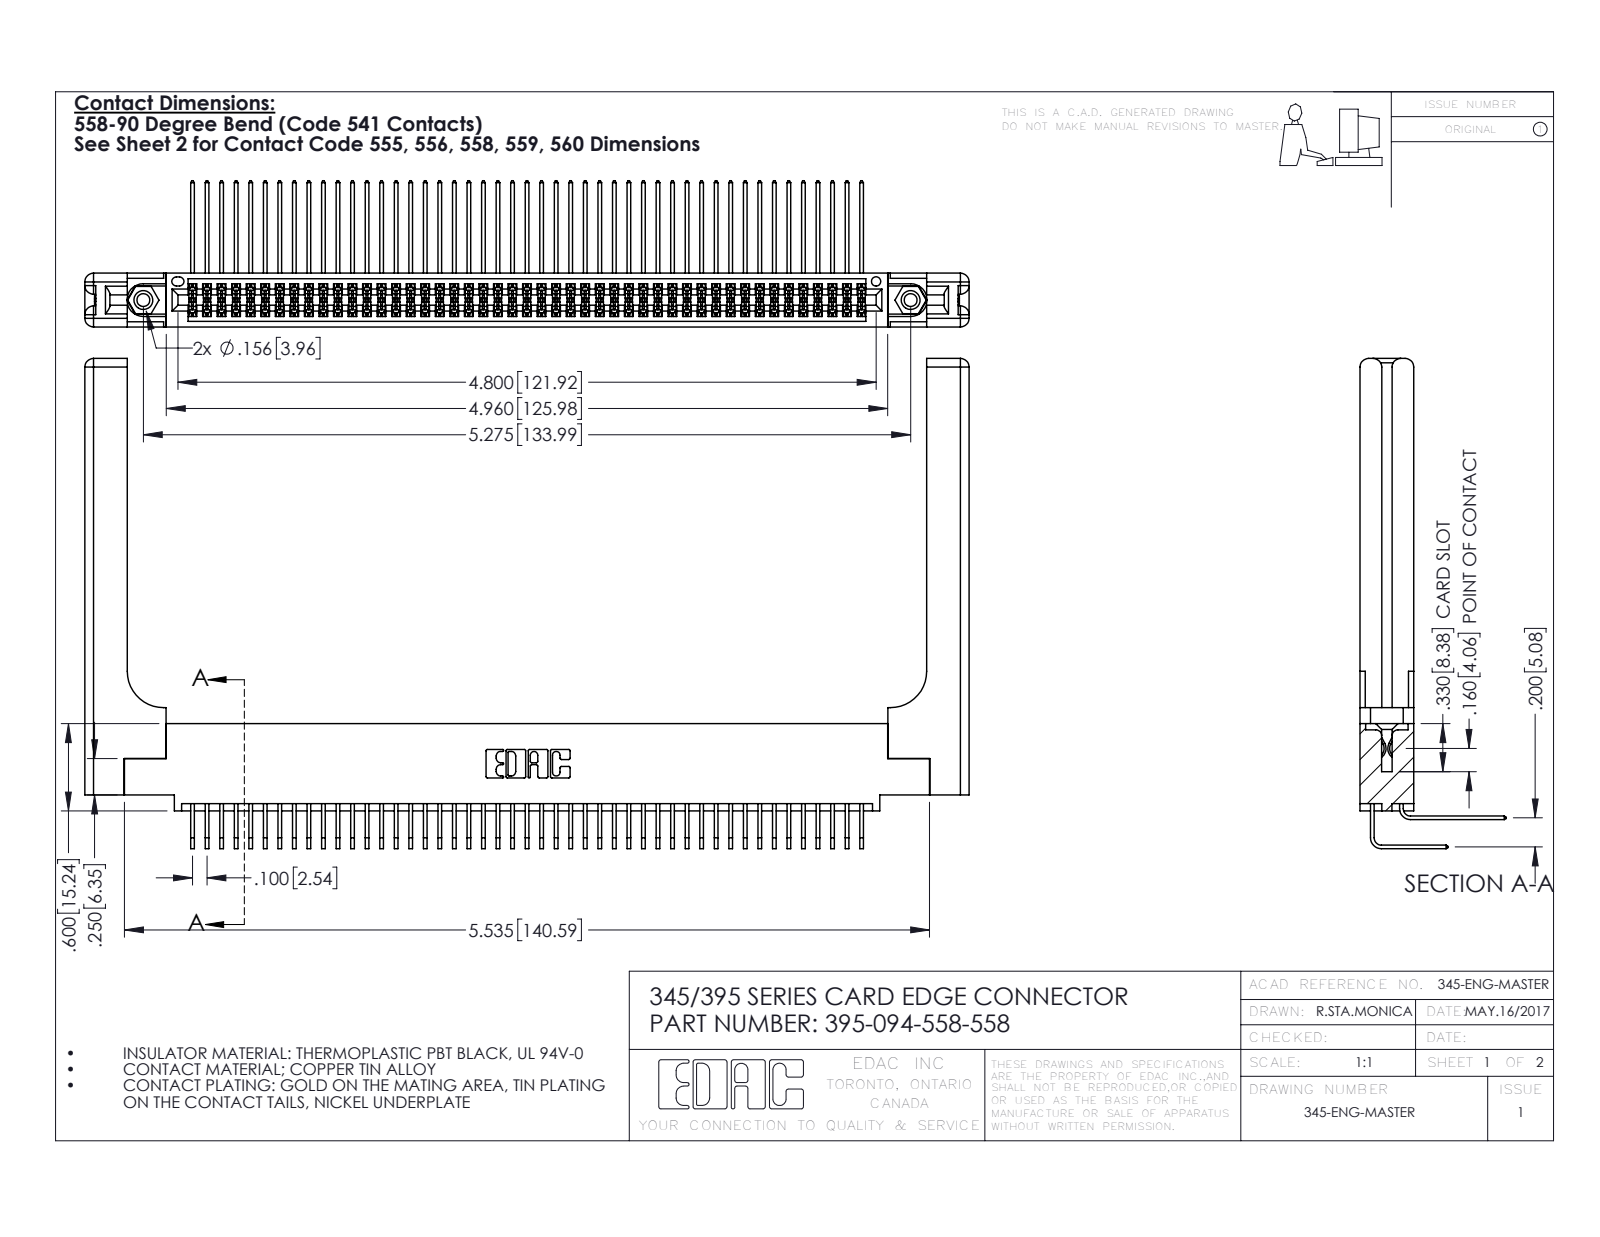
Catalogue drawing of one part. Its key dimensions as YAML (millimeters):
part_name: "345 Part_0.110 Offset - 0.156 Dia-TH; 345-292-001_558 559 Tail - 1; 345-292-001_558 Tail - 2; 345-250-001_345-250-001-102 (+2 more)"
step_written_by: "SolidWorks 2016 (CONFIG_CONTROL_DESIGN)"
units: millimeters
bodies: {solids: 99, faces: 5274, planar: 3522, cylindrical: 1692, other: 60}
overall_size: [154.4, 85.6, 25.5]
volume: 23990
surface_area: 30730
round_holes:
  - {diameter: 2.3, count: 2}
  - {diameter: 3.2, count: 2}
  - {diameter: 4, count: 2}
  - {diameter: 1.6, count: 1}
round_bosses_or_shafts:
  - {diameter: 3.9, count: 2}
partial_cylinders:
  - {radius: 0.2, count: 142}
  - {radius: 0.3, count: 22}
  - {radius: 1.5, count: 16}
  - {radius: 0.2, count: 6}
  - {radius: 0.8, count: 6}
  - {radius: 0.7, count: 3}
  - {radius: 0.4, count: 2}
  - {radius: 0.5, count: 2}
face_to_face_distances: [1.8, 7.6, 9.4, 5.1, 2.5, 6.9, 0.6, 5.7, 3.8, 3.8]
hole_center_spacings: [6.9, 128, 134]
